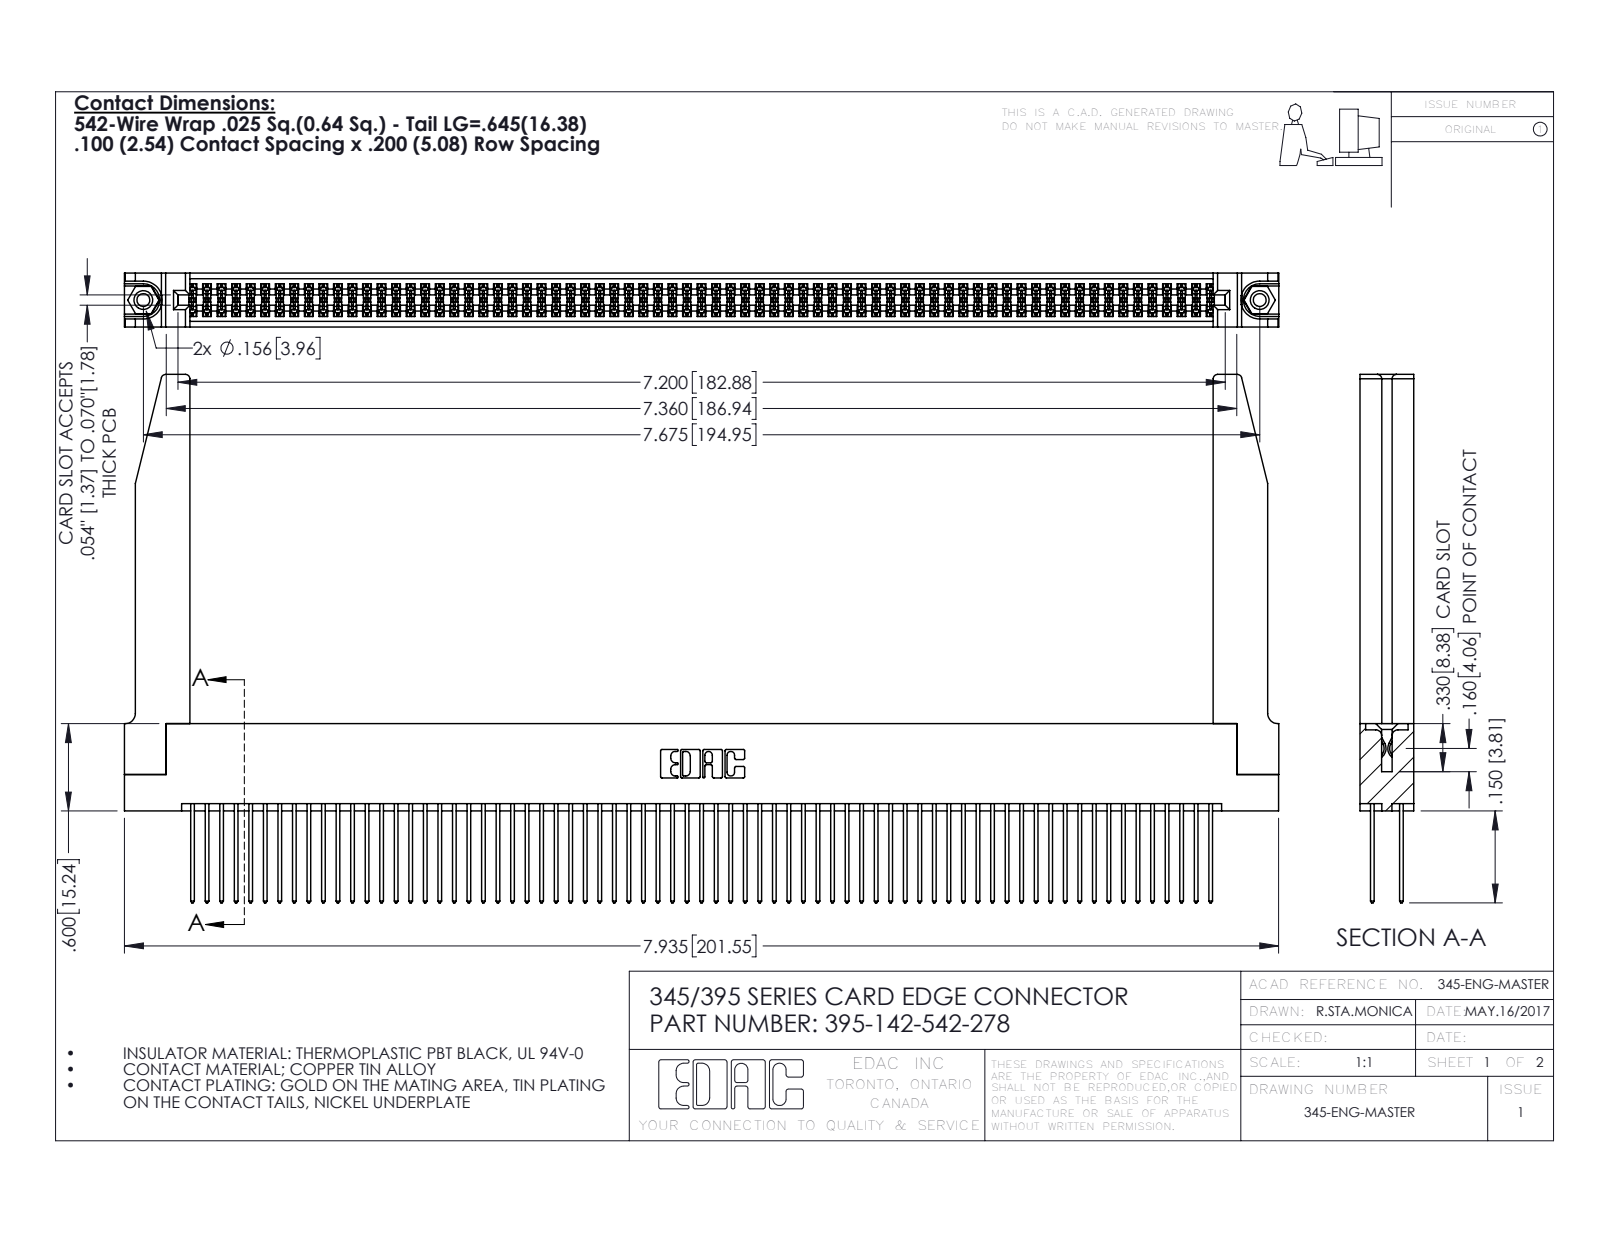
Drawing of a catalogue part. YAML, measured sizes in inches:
part_name: "345 Part_Flush Mounting Lugs - 0.156 Dia-TH; 345-250-001_345-250-001-102; 345-292-001_345-293-142; 395-142-542-278 (+1 more)"
step_written_by: "SolidWorks 2016 (CONFIG_CONTROL_DESIGN)"
units: inches
bodies: {solids: 147, faces: 7460, planar: 4908, cylindrical: 2500, other: 52}
overall_size: [7.936, 3.632, 0.37]
volume: 1.726
surface_area: 63.26
round_holes:
  - {diameter: 0.089, count: 2}
  - {diameter: 0.125, count: 2}
  - {diameter: 0.156, count: 2}
  - {diameter: 0.064, count: 1}
round_bosses_or_shafts:
  - {diameter: 0.155, count: 2}
partial_cylinders:
  - {radius: 0.006, count: 213}
  - {radius: 0.01, count: 142}
  - {radius: 0.01, count: 22}
  - {radius: 0.03, count: 8}
  - {radius: 0.007, count: 6}
  - {radius: 0.031, count: 6}
  - {radius: 0.026, count: 3}
  - {radius: 0.014, count: 2}
face_to_face_distances: [0.072, 0.298, 0.2, 0.37, 0.098, 0.272, 0.025, 0.225, 0.175, 0.149]
hole_center_spacings: [0.27, 7.439, 7.675]
